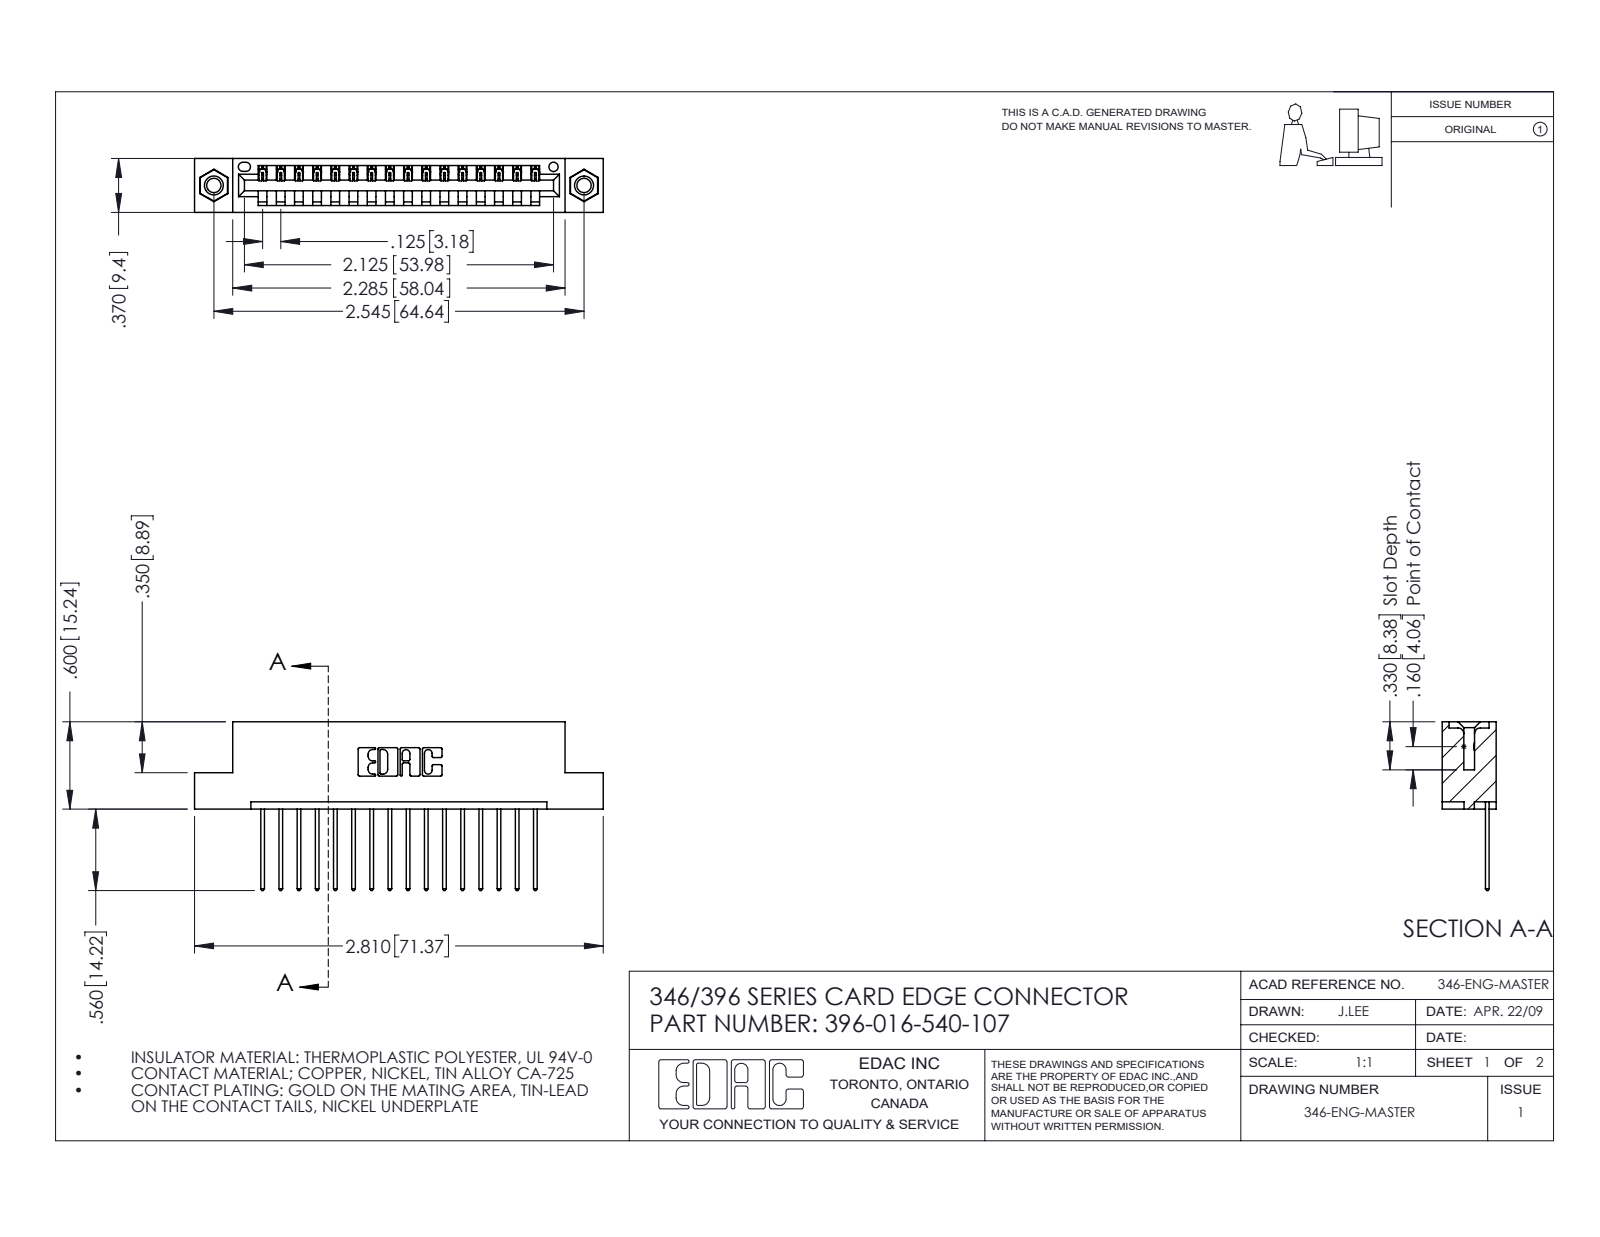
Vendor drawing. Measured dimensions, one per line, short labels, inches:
name: 345-250-001_345-250-005-103; 396-016-540-107; 346 Part_Flush Mounting Lugs - 0.156 Dia-TI; 345-292-001_345-293-140
written by: SolidWorks 2016 (CONFIG_CONTROL_DESIGN)
unit: in
bodies: 19 solids, 1110 faces (748 planar, 346 cylindrical, 16 other)
size: 2.81 × 1.16 × 0.37
volume: 0.406 in³; area: 12.77 in²
holes: 2× ⌀0.098, 2× ⌀0.125, 2× ⌀0.156, 1× ⌀0.064
bosses: 2× ⌀0.155
rounds: 32× R0.006, 32× R0.01, 22× R0.01, 6× R0.007, 6× R0.031, 3× R0.026, 2× R0.031, 2× R0.04
face distances: 0.048, 0.322, 0.25, 0.37, 0.072, 0.298, 0.025, 0.148, 0.222, 0.1
hole spacings: 0.246, 2.338, 2.545
